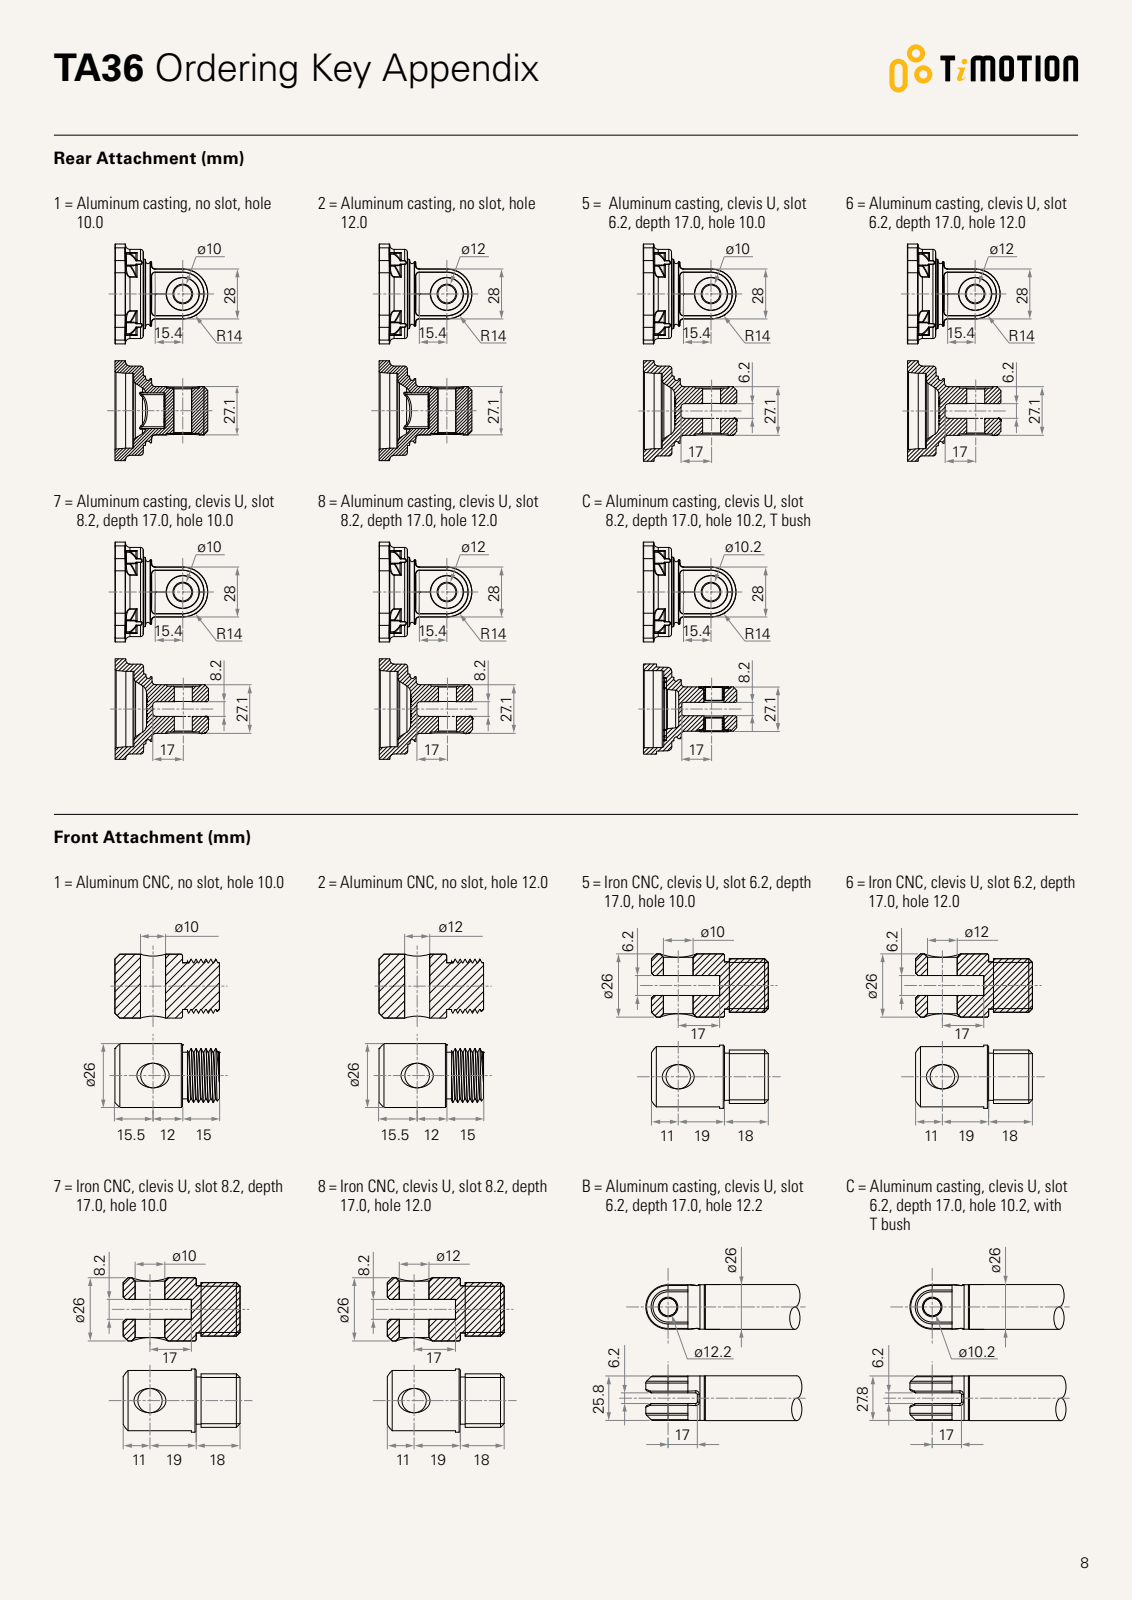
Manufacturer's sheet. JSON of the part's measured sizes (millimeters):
{"part_name": "TA36", "step_written_by": "SolidWorks 2015 (CONFIG_CONTROL_DESIGN)", "units": "millimeters", "bodies": {"solids": 3, "faces": 550, "planar": 159, "cylindrical": 131, "other": 260}, "overall_size": [499.5, 179, 95.23], "volume_mm3": 1924000, "surface_area_mm2": 230035, "round_holes": [[10.01, 2], [26, 1], [36.1, 1]], "round_bosses_or_shafts": [[7.3, 6], [6.8, 3], [36, 1], [26.1, 1], [20, 1], [5.5, 1]], "partial_cylinders_radius": [[0.2, 44], [1, 22], [3.5, 3], [14, 1]], "face_to_face_distances": [60.5, 64.5, 4, 424.5, 360, 420.5, 9.45, 17.65, 5, 365], "hole_center_spacings": [470]}
